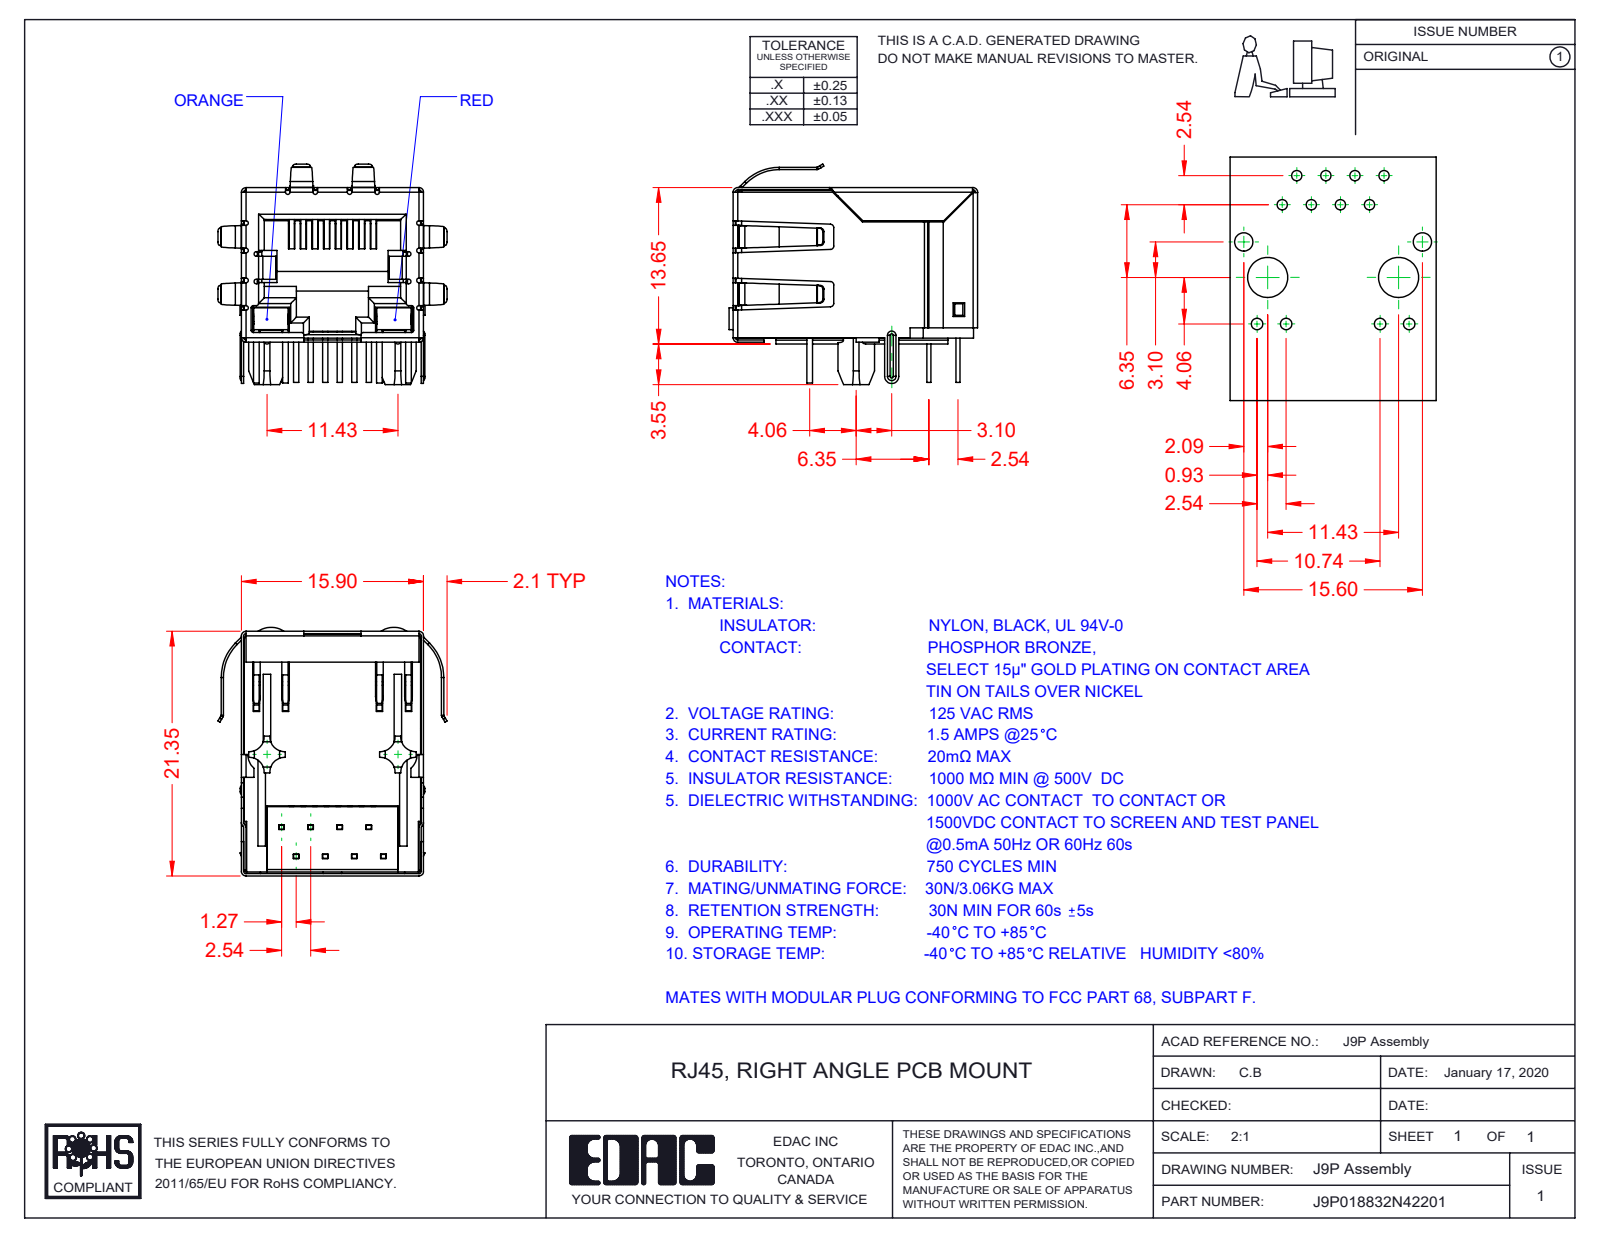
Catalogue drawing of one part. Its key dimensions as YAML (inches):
part_name: "9P-LED Shield; 9P-LED Assembly; 9P-LED Insulator; 9P-LED LED LH_4-Orange (+4 more)"
step_written_by: "SolidWorks 2016 (CONFIG_CONTROL_DESIGN)"
units: inches
bodies: {solids: 13, faces: 1472, planar: 1042, cylindrical: 336, other: 94}
overall_size: [0.854, 0.787, 0.758]
volume: 0.164
surface_area: 11.65
partial_cylinders:
  - {radius: 0.008, count: 39}
  - {radius: 0.02, count: 22}
  - {radius: 0.012, count: 20}
  - {radius: 0.016, count: 16}
  - {radius: 0.051, count: 8}
  - {radius: 0.009, count: 5}
  - {radius: 0.004, count: 4}
  - {radius: 0.012, count: 4}
face_to_face_distances: [0.608, 0.618, 0.616, 0.014, 0.021, 0.61, 0.487, 0.024, 0.055, 0.023]
